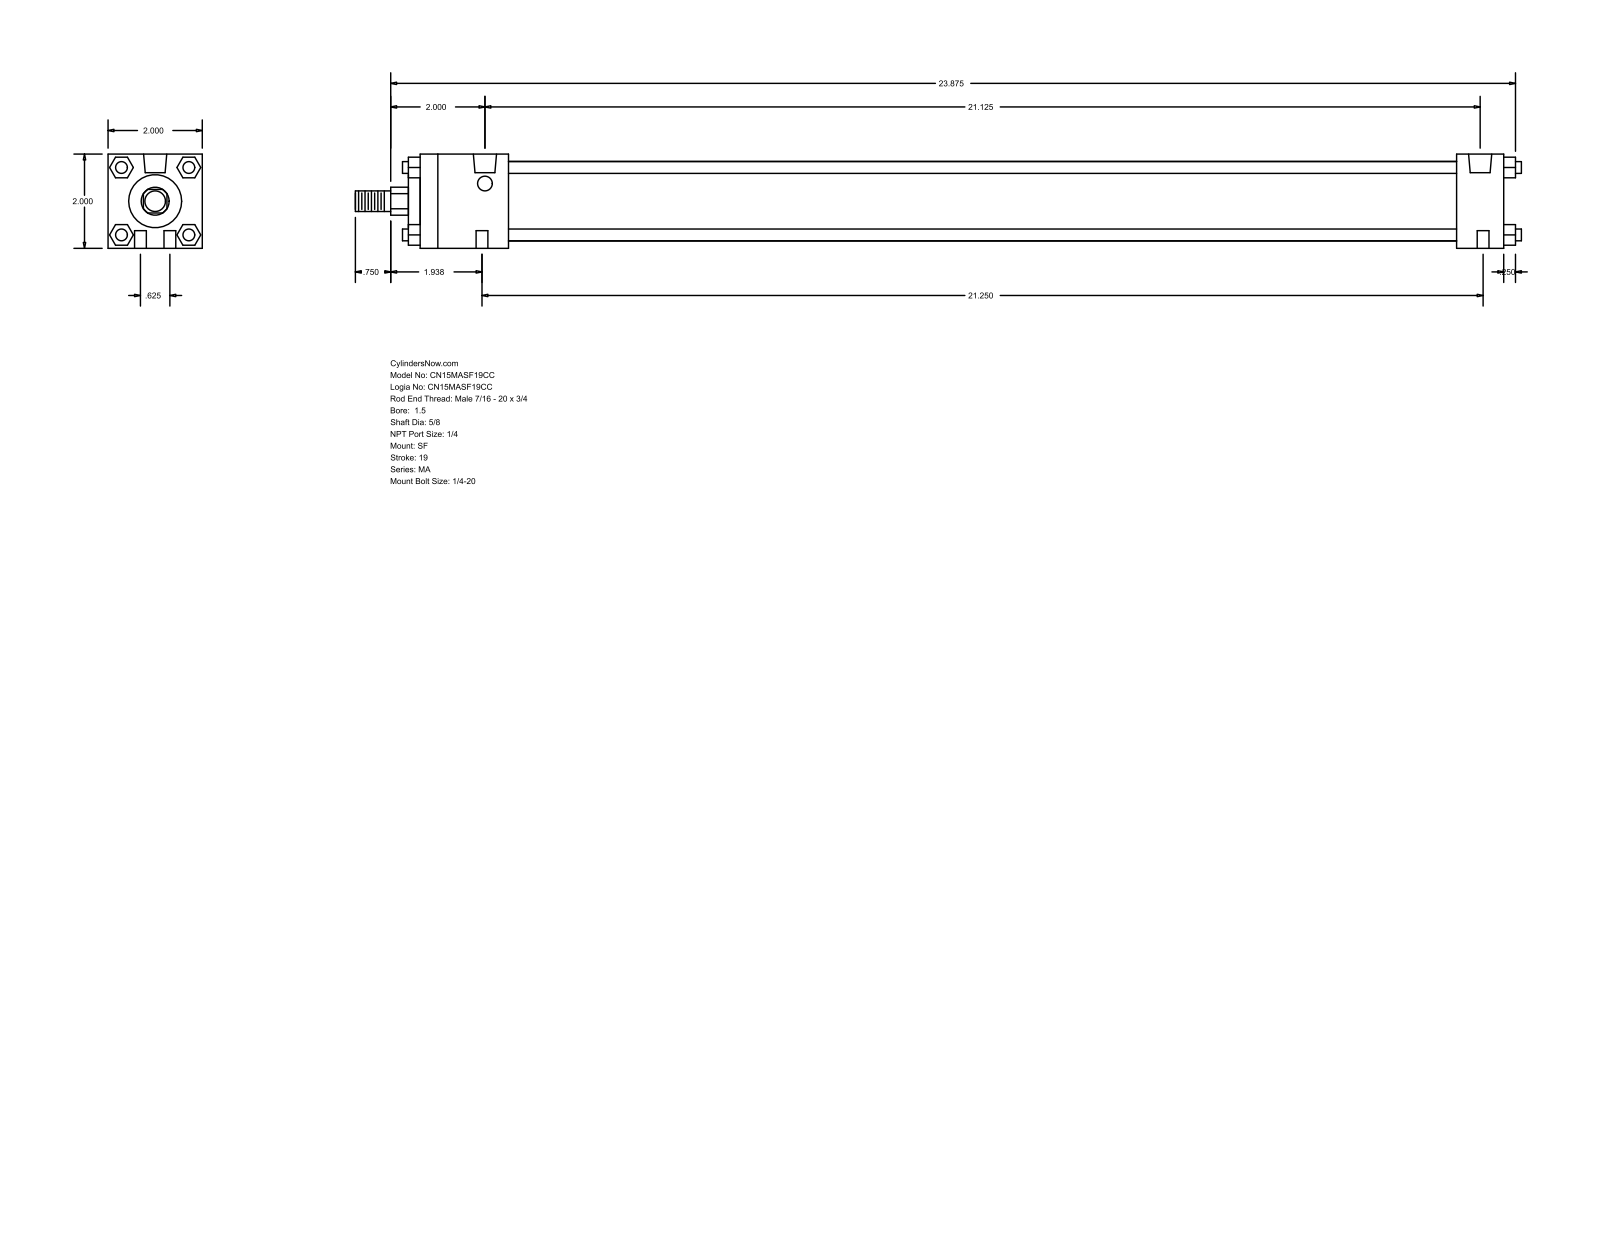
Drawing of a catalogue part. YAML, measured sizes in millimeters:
part_name: "MA_SF__0150_0.625"
step_written_by: "GSSL Pune (CONFIG_CONTROL_DESIGN)"
units: millimeters
bodies: {solids: 0, faces: 124, planar: 94, cylindrical: 30, other: 0}
overall_size: [628.65, 50.8, 50.8]
round_holes:
  - {diameter: 6.35, count: 4}
  - {diameter: 7.94, count: 2}
  - {diameter: 12.49, count: 2}
round_bosses_or_shafts:
  - {diameter: 6.35, count: 4}
  - {diameter: 42.93, count: 1}
  - {diameter: 28.57, count: 1}
  - {diameter: 15.88, count: 1}
  - {diameter: 11.11, count: 1}
partial_cylinders:
  - {radius: 7.54, count: 1}
face_to_face_distances: [50.8, 584.2, 47.62, 558.79, 511.17, 536.58, 25.41, 6.35, 53.97, 565.14]
hole_center_spacings: [8.1, 15.88, 536.58, 538.22, 538.23, 539.75, 539.98]
